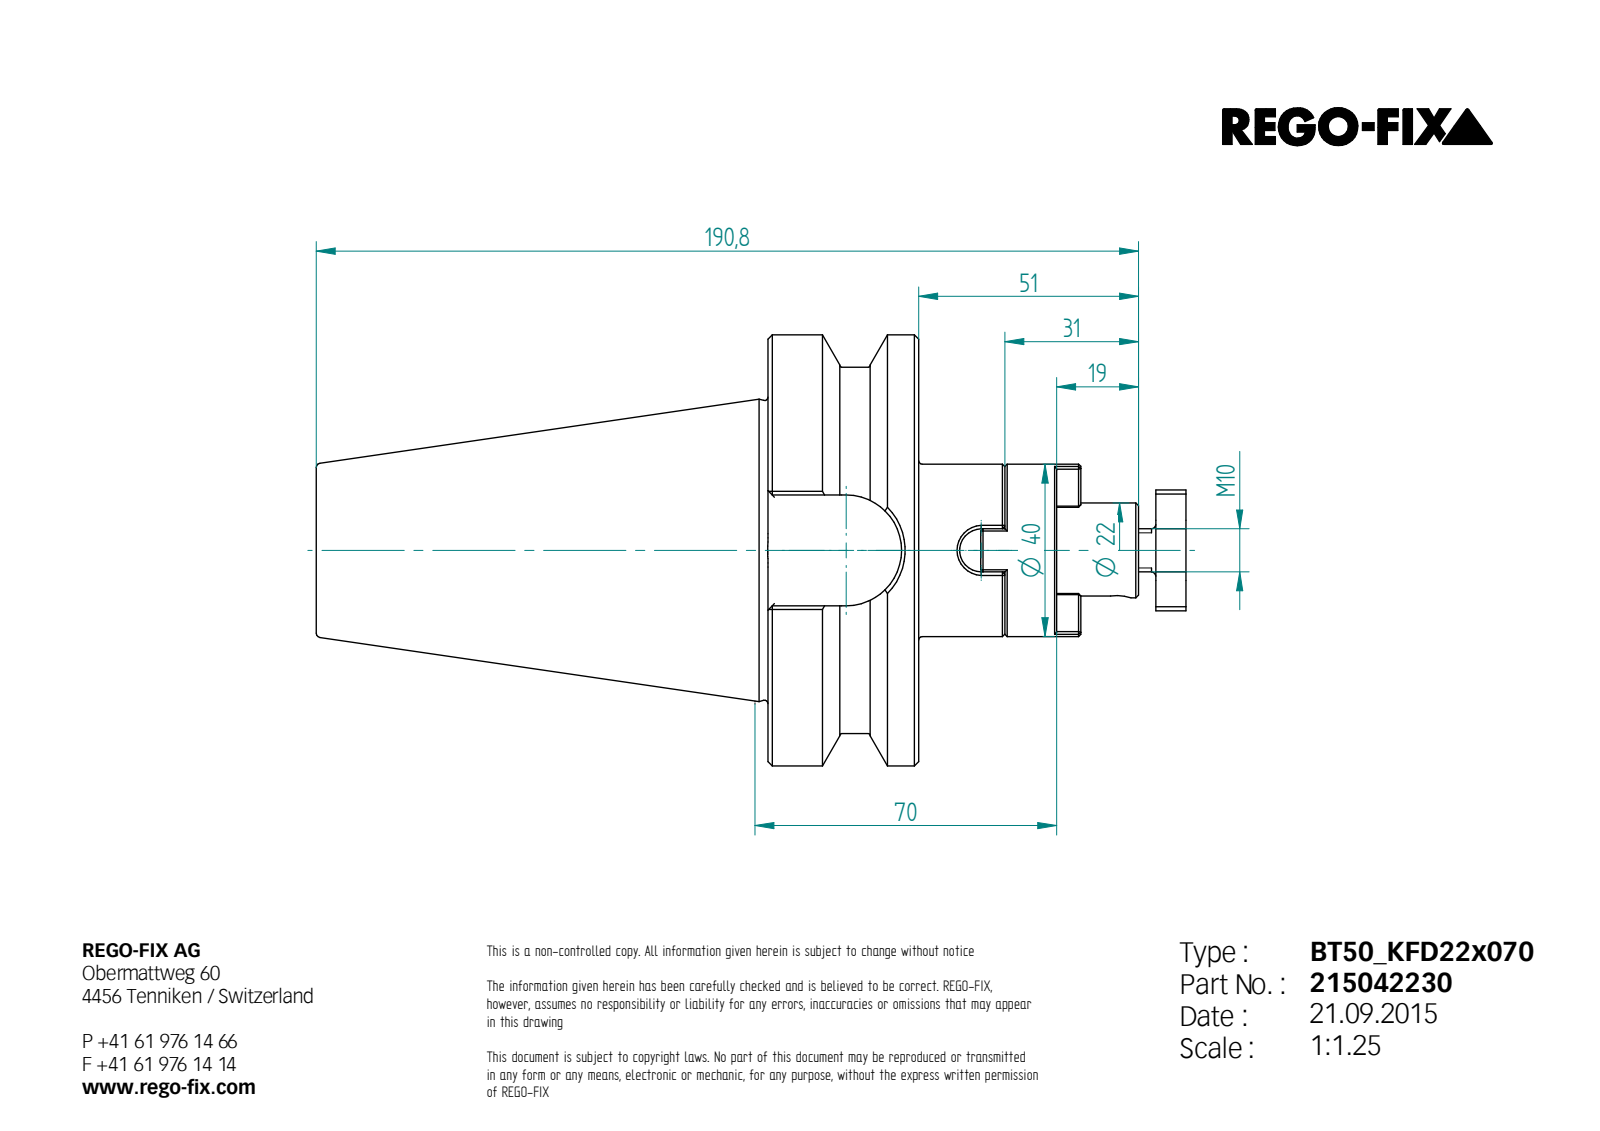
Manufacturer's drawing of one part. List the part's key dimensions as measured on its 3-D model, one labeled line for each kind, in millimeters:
STEP written by: Unknown (AUTOMOTIVE_DESIGN)
Units: millimetres
Bodies: 3 solids, 207 faces (118 planar, 35 cylindrical, 54 other)
Overall size (bounding box): 201.8 × 100 × 100
Volume: 492 454 mm³ · Surface area: 66 967 mm²
Round holes (diameter × count): ⌀8.38 ×1, ⌀10.5 ×1, ⌀20.75 ×1, ⌀22 ×1, ⌀25 ×1
Round bosses / shafts (diameter × count): ⌀100 ×1, ⌀85 ×1, ⌀40 ×1, ⌀21.4 ×1, ⌀10 ×1
Partial cylindrical surfaces — rounded edges, fillets, slot ends (radius × count): R0.5 ×4, R2 ×4, R3 ×2, R5 ×1, R12.85 ×1, R14 ×1
Main face-to-face distances: 35, 55, 20, 70.7, 67, 32, 12, 104.8, 139.8, 159.8
